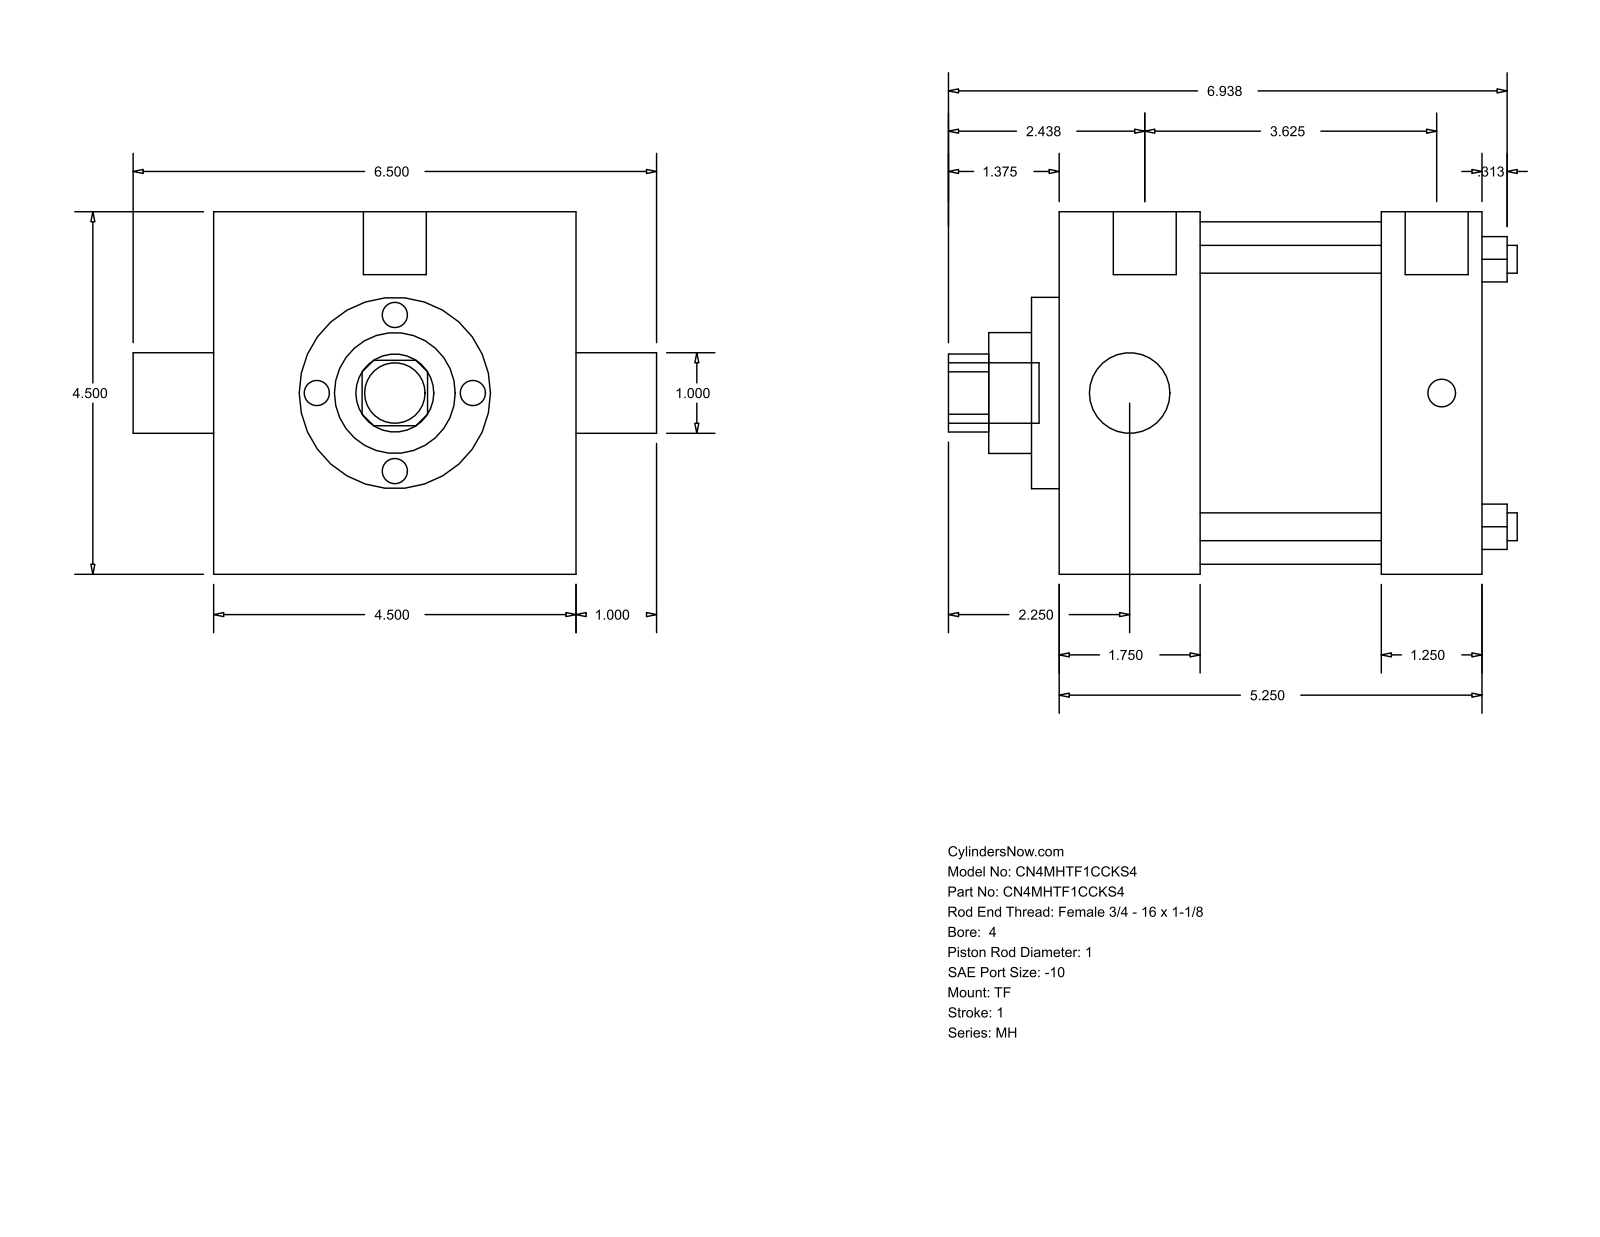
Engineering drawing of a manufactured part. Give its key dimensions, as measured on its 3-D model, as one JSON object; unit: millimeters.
{"part_name": "MH_TF__0400_1", "step_written_by": "GSSL Pune (CONFIG_CONTROL_DESIGN)", "units": "millimeters", "bodies": {"solids": 0, "faces": 86, "planar": 61, "cylindrical": 25, "other": 0}, "overall_size": [179.39, 165.1, 114.3], "round_holes": [[8.76, 4], [25.4, 2], [38.1, 1], [60.33, 1], [107.95, 1]], "round_bosses_or_shafts": [[8.73, 3], [19.84, 2], [19.05, 1]], "partial_cylinders_radius": [[12.29, 1]], "face_to_face_distances": [114.3, 133.36, 44.46, 88.9, 101.61, 57.15, 31.75, 8.73, 53.19, 110.34], "hole_center_spacings": [59.62, 84.32, 119.25]}
